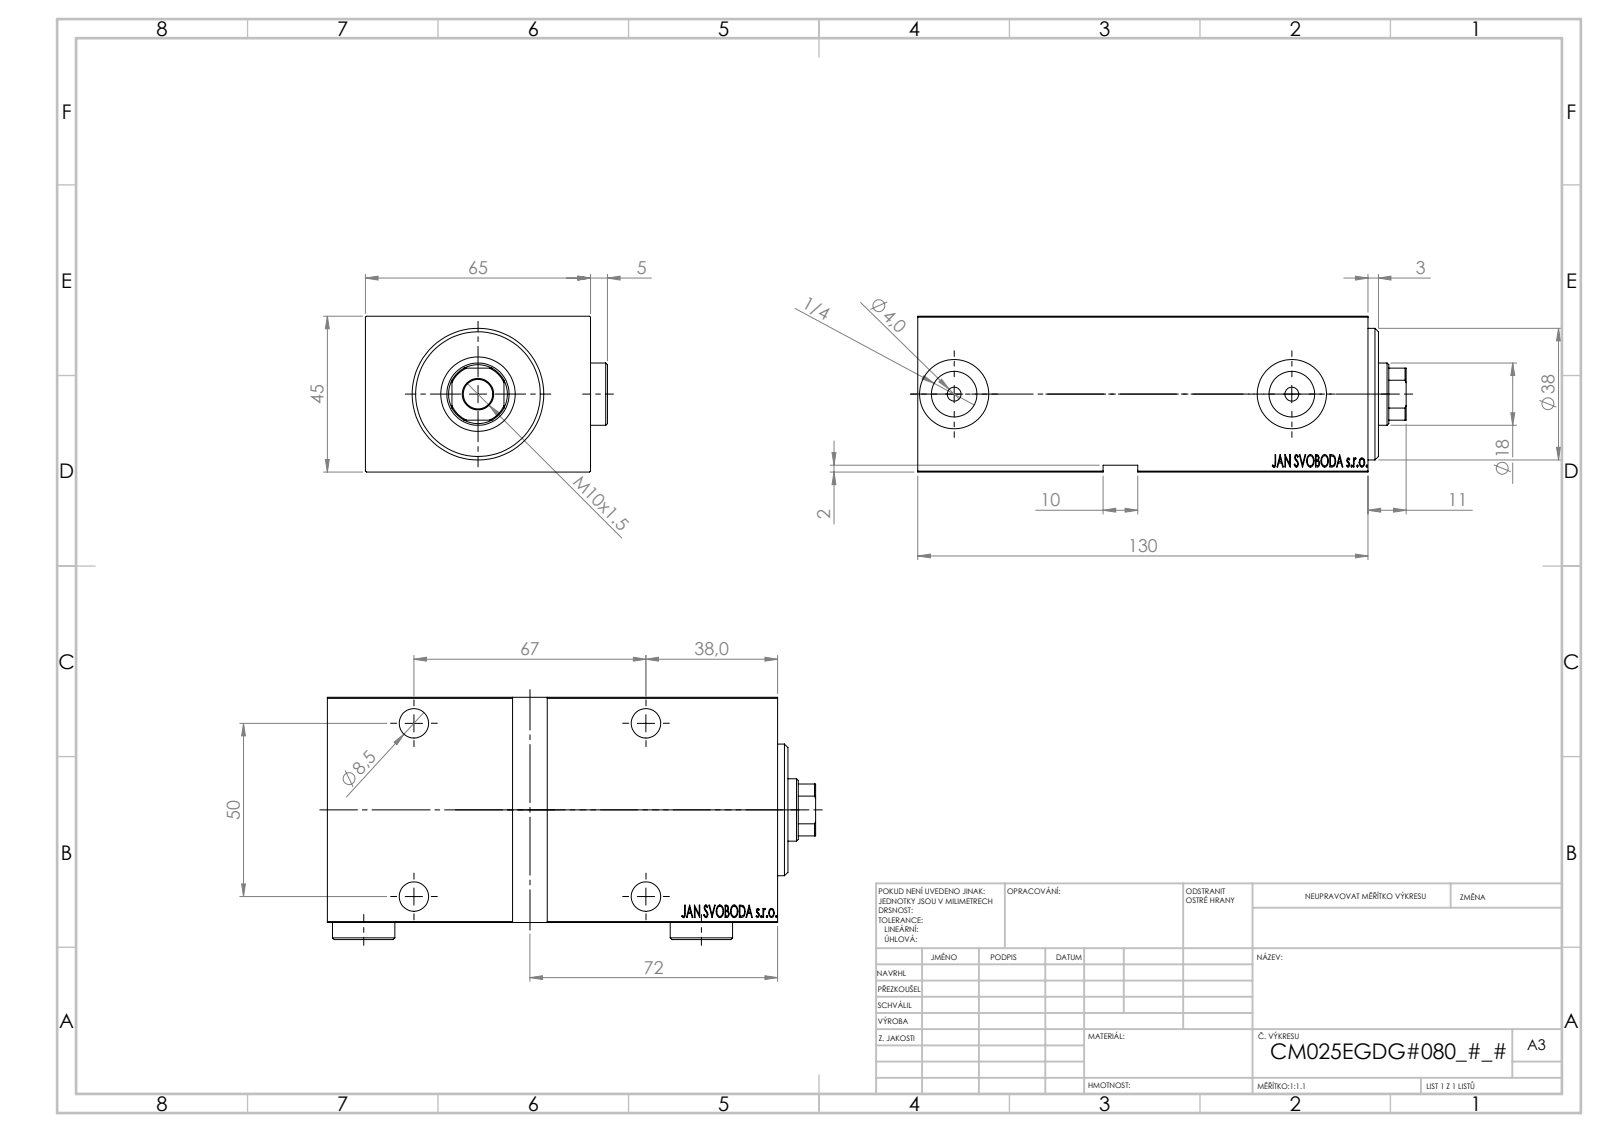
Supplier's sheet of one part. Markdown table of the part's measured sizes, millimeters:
| quantity | value |
| --- | --- |
| part name | V450CM_E_Body; V450CM_E_VCP; V450CM_VC_B; Zatka_OIL_PORT |
| STEP written by | SolidWorks 2019 (CONFIG_CONTROL_DESIGN) |
| units | millimeters |
| bodies | 5 solids, 910 faces (444 planar, 68 cylindrical, 398 other) |
| overall size | 141 × 69.9 × 45 |
| volume | 346 692 mm³ |
| surface area | 68 165 mm² |
| round holes (diameter × count) | 8.5 × 5, 13.5 × 4, 4 × 2, 13.16 × 2, 20 × 2, 18 × 1, 21.5 × 1, 25 × 1, 35 × 1 |
| round bosses / shafts (diameter × count) | 18 × 2, 38 × 1, 27 × 1 |
| partial cylindrical surfaces (radius × count) | 8.5 × 1 |
| main face-to-face distances | 45, 65, 130, 5, 64.9, 6, 124, 125, 119, 8 |
| hole center spacings | 50, 67, 83.6, 97.5 |
